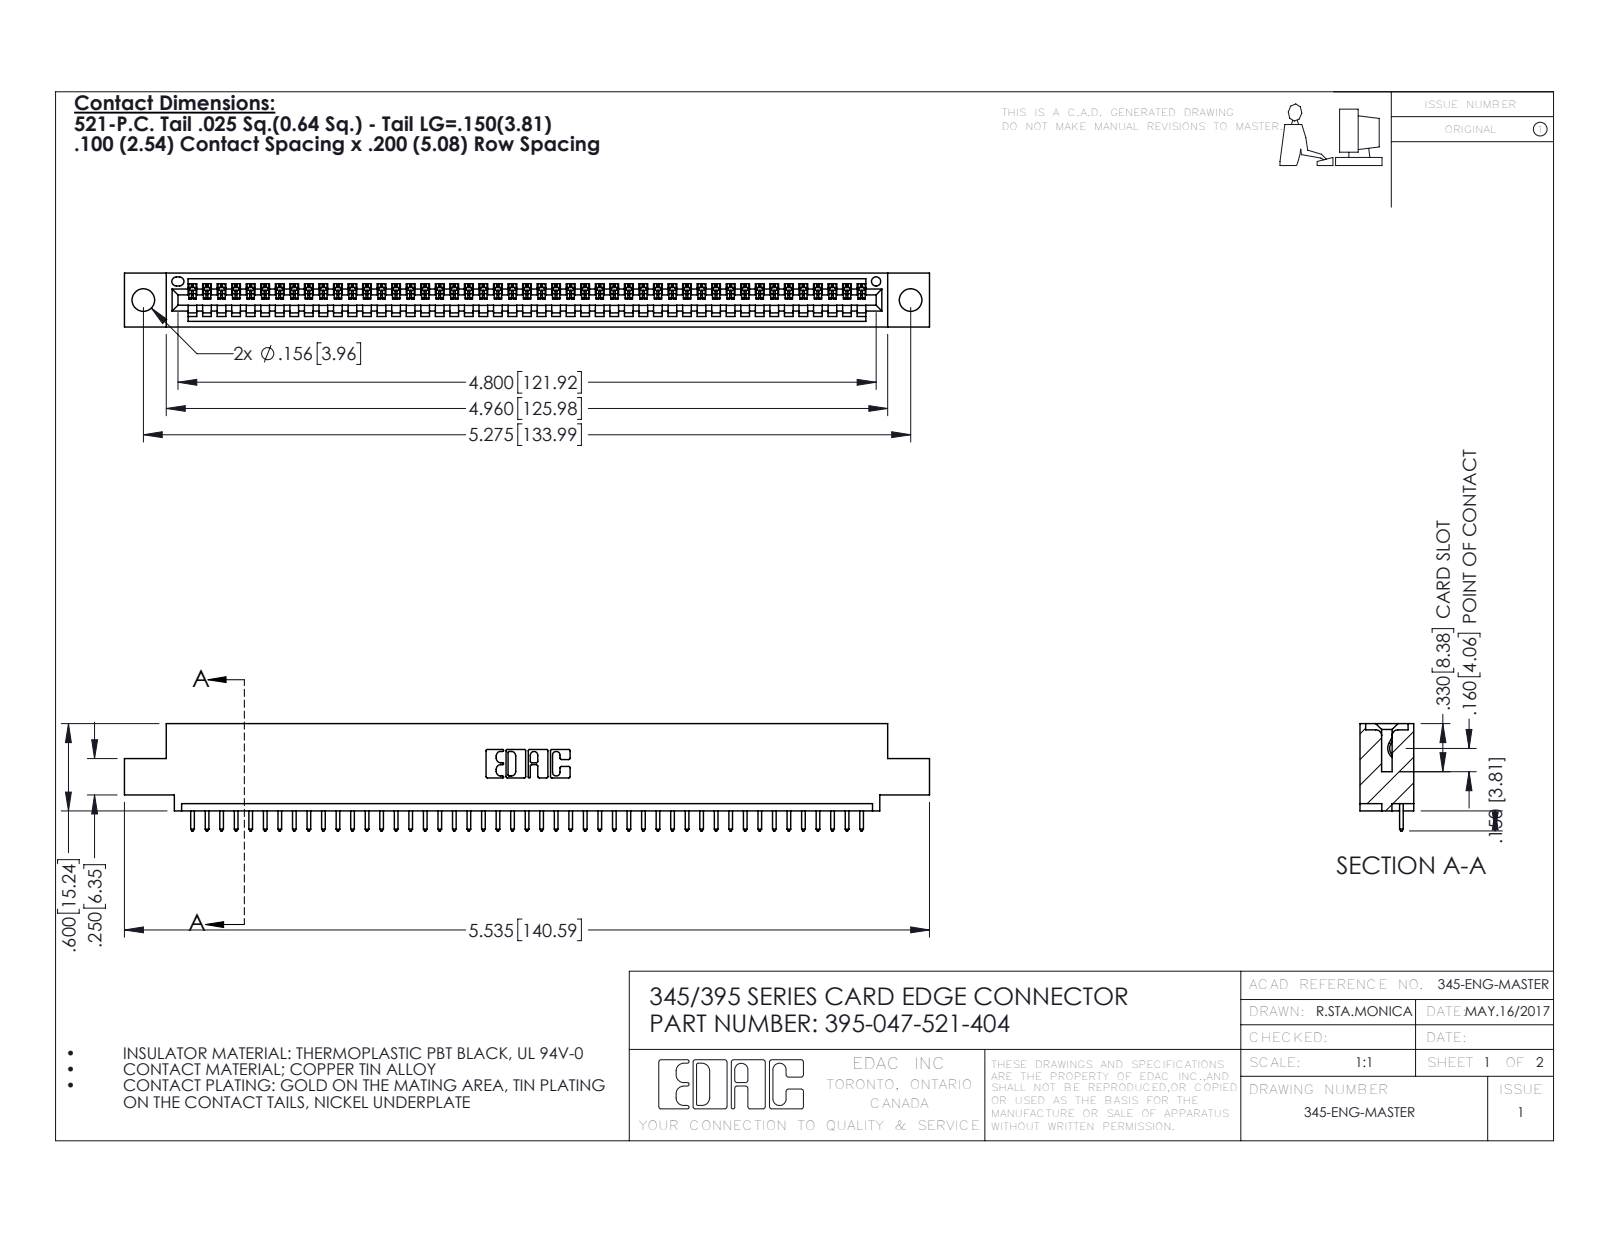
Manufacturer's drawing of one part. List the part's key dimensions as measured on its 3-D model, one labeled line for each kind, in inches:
Part name (STEP PRODUCT): 345 Part_0.110 Offset - 0.156 Dia-TH; 345-292-001_345-293-121; 395-047-521-404
STEP written by: SolidWorks 2016 (CONFIG_CONTROL_DESIGN)
Units: inches
Bodies: 48 solids, 2856 faces (1964 planar, 892 cylindrical, 0 other)
Overall size (bounding box): 5.535 × 0.737 × 0.37
Volume: 0.799 in³ · Surface area: 26.11 in²
Round holes (diameter × count): ⌀0.156 ×2, ⌀0.064 ×1
Partial cylindrical surfaces — rounded edges, fillets, slot ends (radius × count): R0.006 ×94, R0.01 ×94, R0.01 ×22, R0.007 ×6, R0.031 ×6, R0.026 ×3, R0.031 ×2, R0.04 ×2
Main face-to-face distances: 0.298, 0.072, 0.37, 0.2, 0.098, 0.272, 0.025, 0.225, 0.149, 0.072
Hole centre spacings: 0.27, 5.039, 5.275
